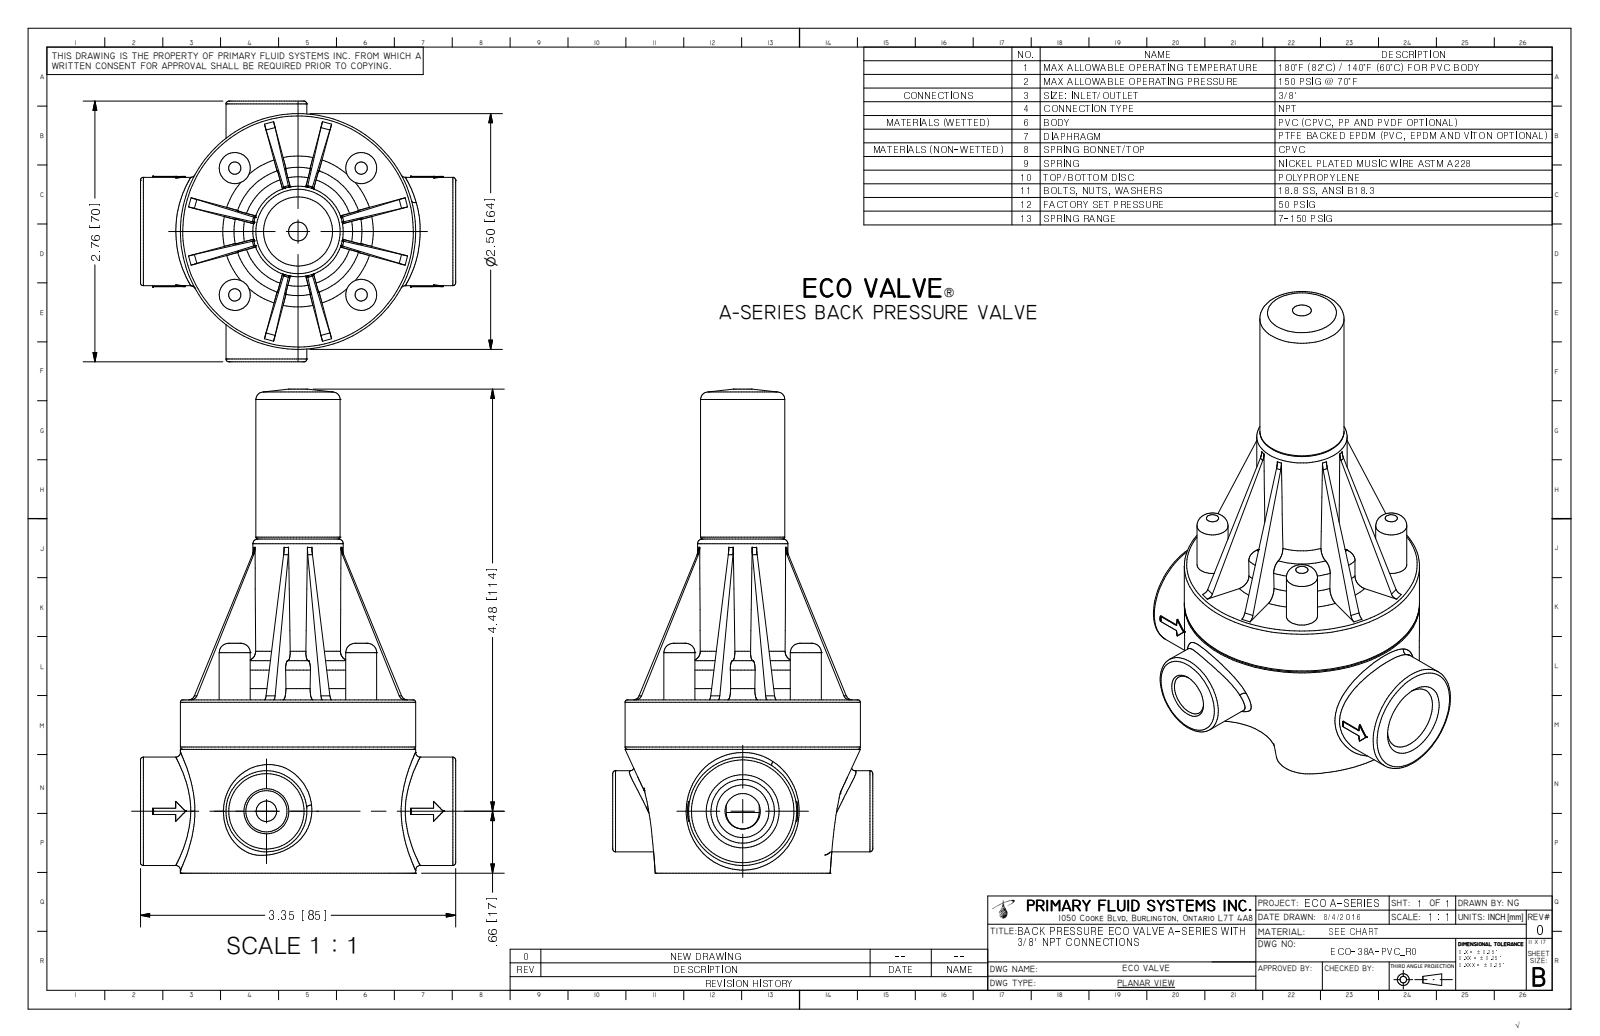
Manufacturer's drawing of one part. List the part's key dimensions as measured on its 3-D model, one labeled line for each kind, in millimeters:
Part name (STEP PRODUCT): ECO-38A-PVC_R0
STEP written by: Autodesk Inventor 2009 (AUTOMOTIVE_DESIGN)
Units: millimetres
Bodies: 1 solid, 308 faces (125 planar, 72 cylindrical, 111 other)
Overall size (bounding box): 130.4 × 85.1 × 70.2
Volume: 194 500 mm³ · Surface area: 40 590 mm²
Round holes (diameter × count): ⌀5.8 ×4, ⌀6.5 ×4, ⌀10.2 ×4, ⌀11.1 ×1
Round bosses / shafts (diameter × count): ⌀8.4 ×4, ⌀6.5 ×4, ⌀63.5 ×1, ⌀34.5 ×1, ⌀29.2 ×1, ⌀24.4 ×1, ⌀22.7 ×1, ⌀21.8 ×1
Partial cylindrical surfaces — rounded edges, fillets, slot ends (radius × count): R1.8 ×8, R2.5 ×8, R3.3 ×4, R12.9 ×1, R14.8 ×1, R23.3 ×1, R27.1 ×1
Main face-to-face distances: 46.7, 33.4, 13.3, 5.1, 28.3, 41.6, 6.9, 85.1, 3.8, 29.5
Hole centre spacings: 34.1, 48.3, 34.1, 34.1, 48.3, 48.3
